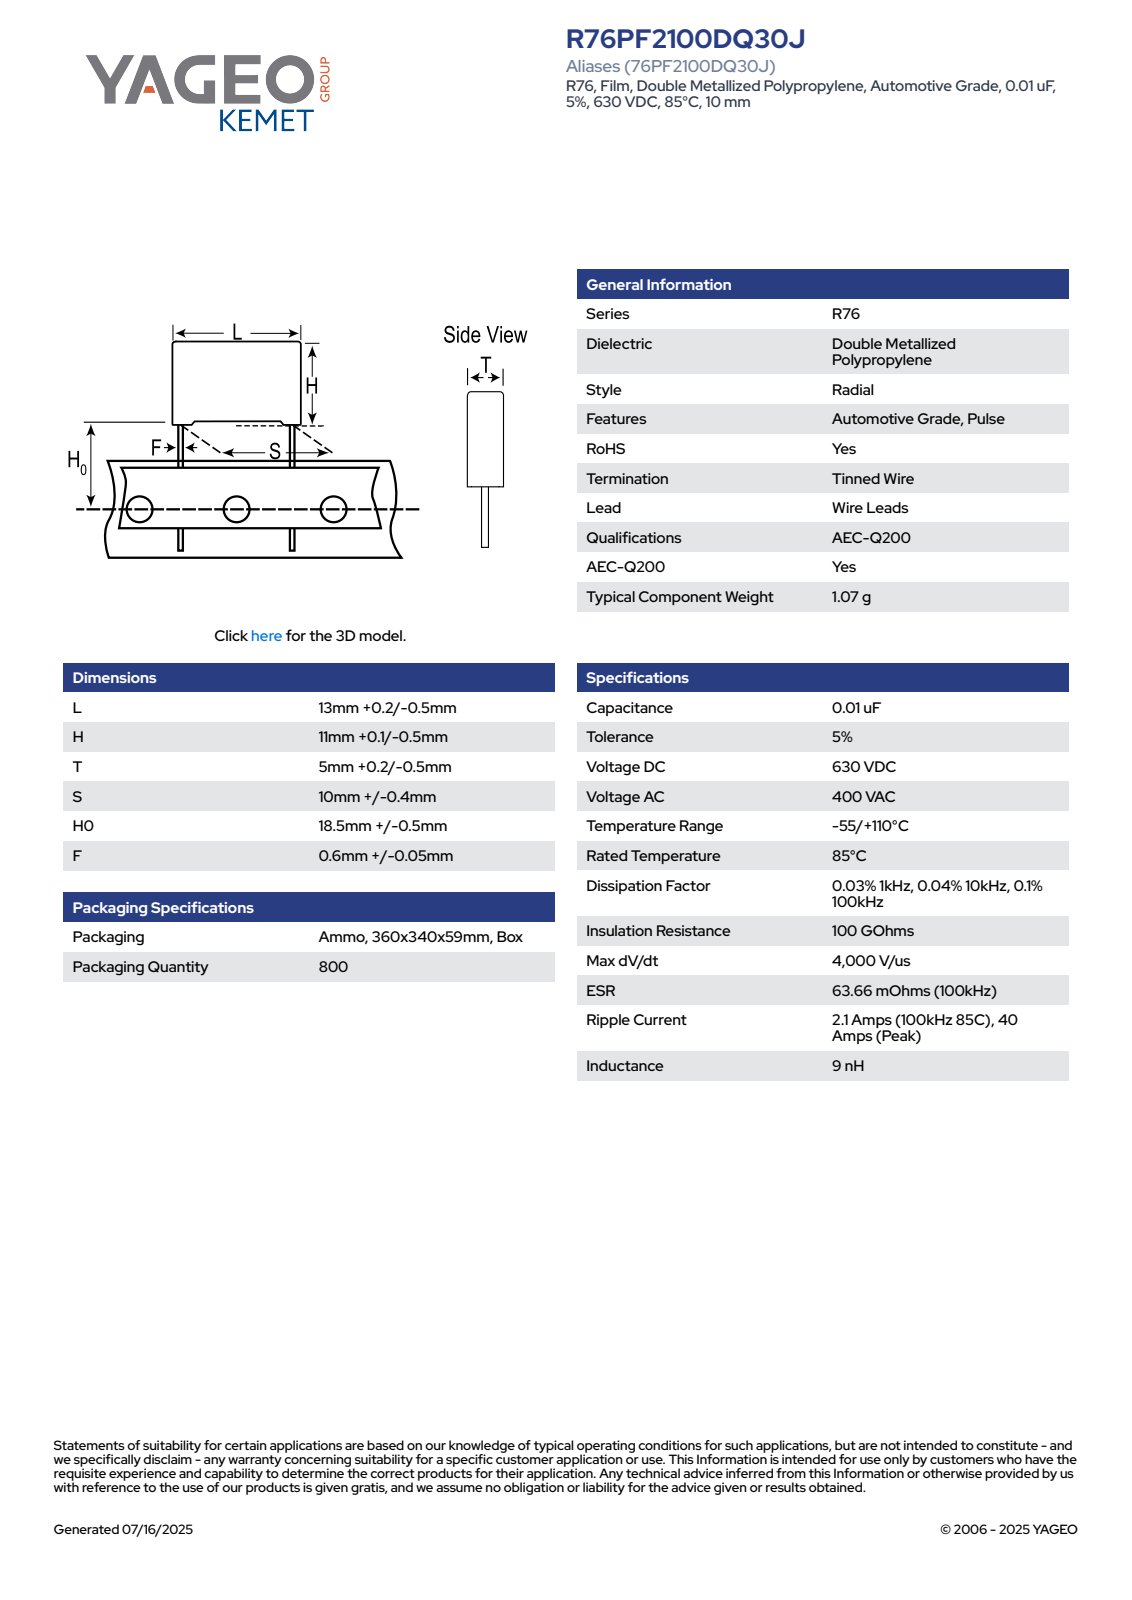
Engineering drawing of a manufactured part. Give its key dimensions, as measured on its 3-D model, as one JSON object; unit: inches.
{"part_name": "CFR_RB2_13X11X5_L13.2H11.1T5.2S10H019F0.65", "step_written_by": "SolidWorks 2020 (AUTOMOTIVE_DESIGN)", "units": "inches", "bodies": {"solids": 4, "faces": 85, "planar": 77, "cylindrical": 8, "other": 0}, "overall_size": [1.185, 0.52, 0.205], "volume_in3": 0.045, "surface_area_in2": 1, "round_bosses_or_shafts": [[0.026, 2]], "partial_cylinders_radius": [[0.02, 4]], "face_to_face_distances": [0.205, 0.52, 0.407, 0.017, 0.187, 0.03, 0.437, 0.17, 0.502, 0.015]}
